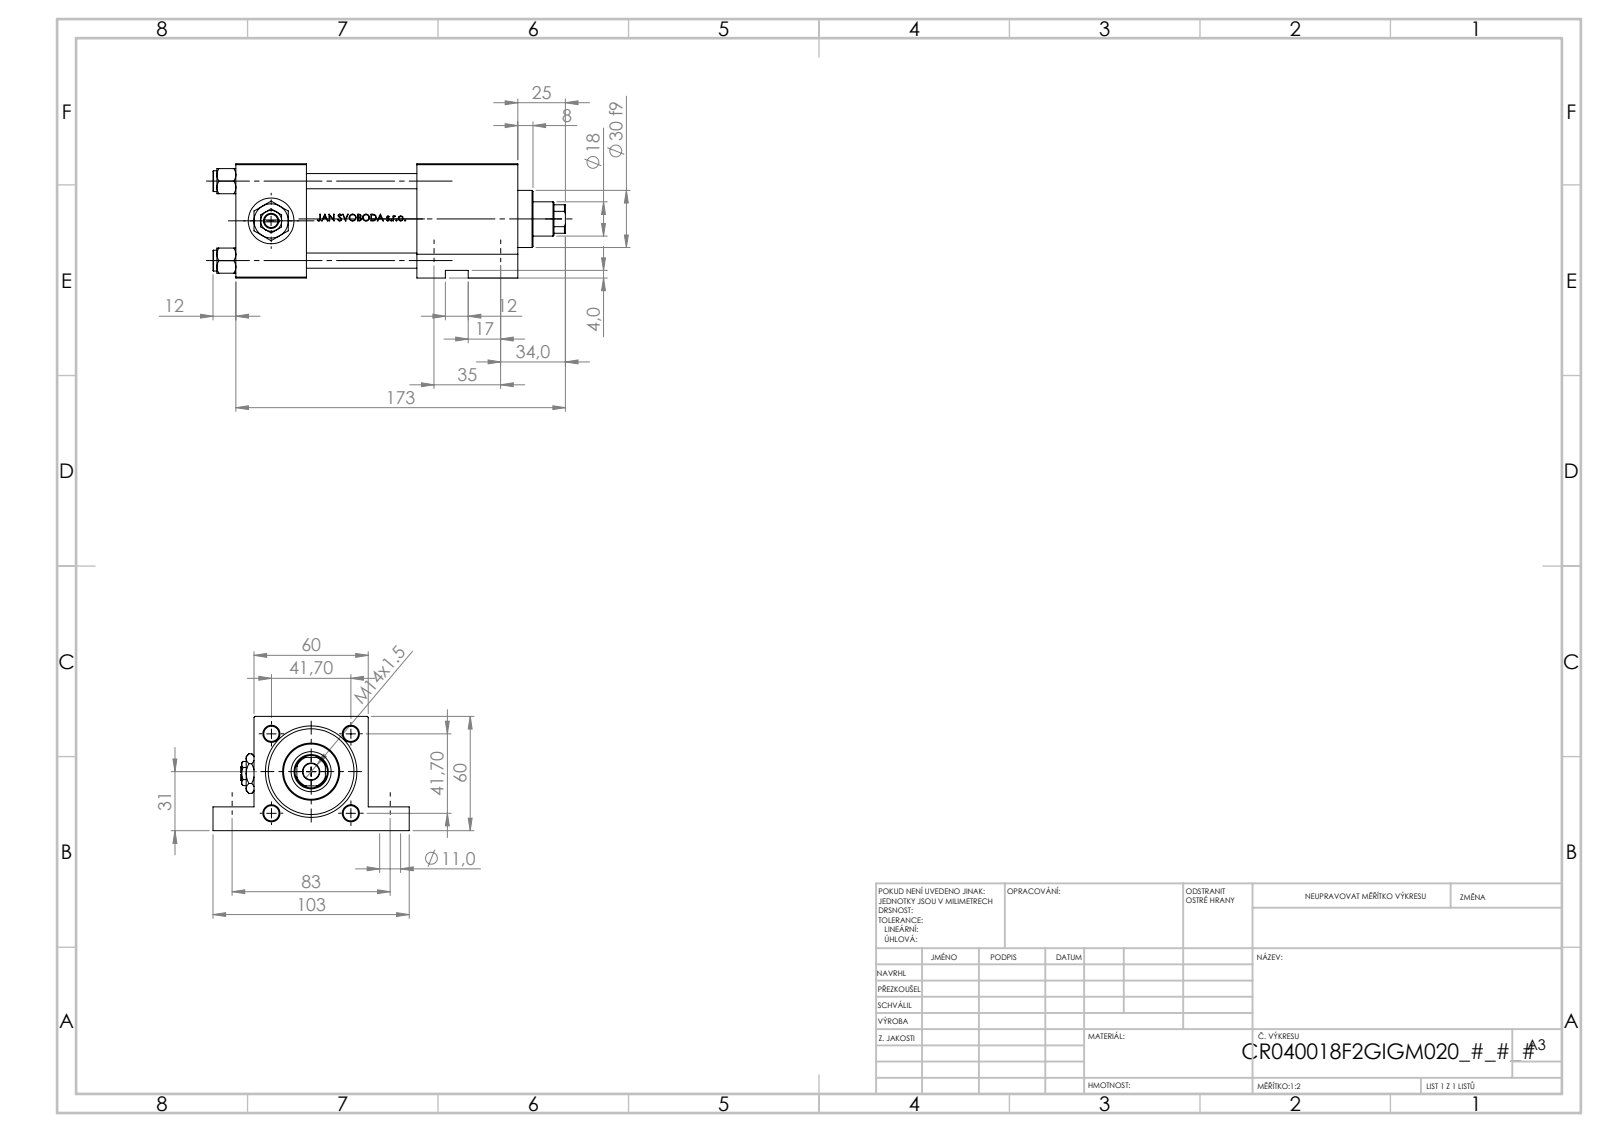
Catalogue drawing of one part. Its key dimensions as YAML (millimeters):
part_name: "Zatka_pro_OIL_PORT; V215CR_F_TYCINKA; NUT_M5_F; V215CR_F_Body (+2 more)"
step_written_by: "SolidWorks 2019 (CONFIG_CONTROL_DESIGN)"
units: millimeters
bodies: {solids: 12, faces: 1167, planar: 460, cylindrical: 145, other: 562}
overall_size: [185, 103, 60]
volume: 421523
surface_area: 113489
round_holes:
  - {diameter: 8, count: 4}
  - {diameter: 7, count: 2}
  - {diameter: 11, count: 2}
  - {diameter: 11, count: 2}
  - {diameter: 16.66, count: 2}
  - {diameter: 24, count: 2}
  - {diameter: 8.5, count: 1}
  - {diameter: 16, count: 1}
  - {diameter: 18, count: 1}
  - {diameter: 21, count: 1}
  - {diameter: 31, count: 1}
  - {diameter: 40, count: 1}
round_bosses_or_shafts:
  - {diameter: 11, count: 4}
  - {diameter: 46, count: 1}
  - {diameter: 30, count: 1}
partial_cylinders:
  - {radius: 8.5, count: 1}
face_to_face_distances: [60, 37, 148, 111, 58, 95, 53, 119.3, 82.3, 24.3]
hole_center_spacings: [41.7, 28.79, 30.2, 35, 42.09, 50.06, 58.97, 83]
